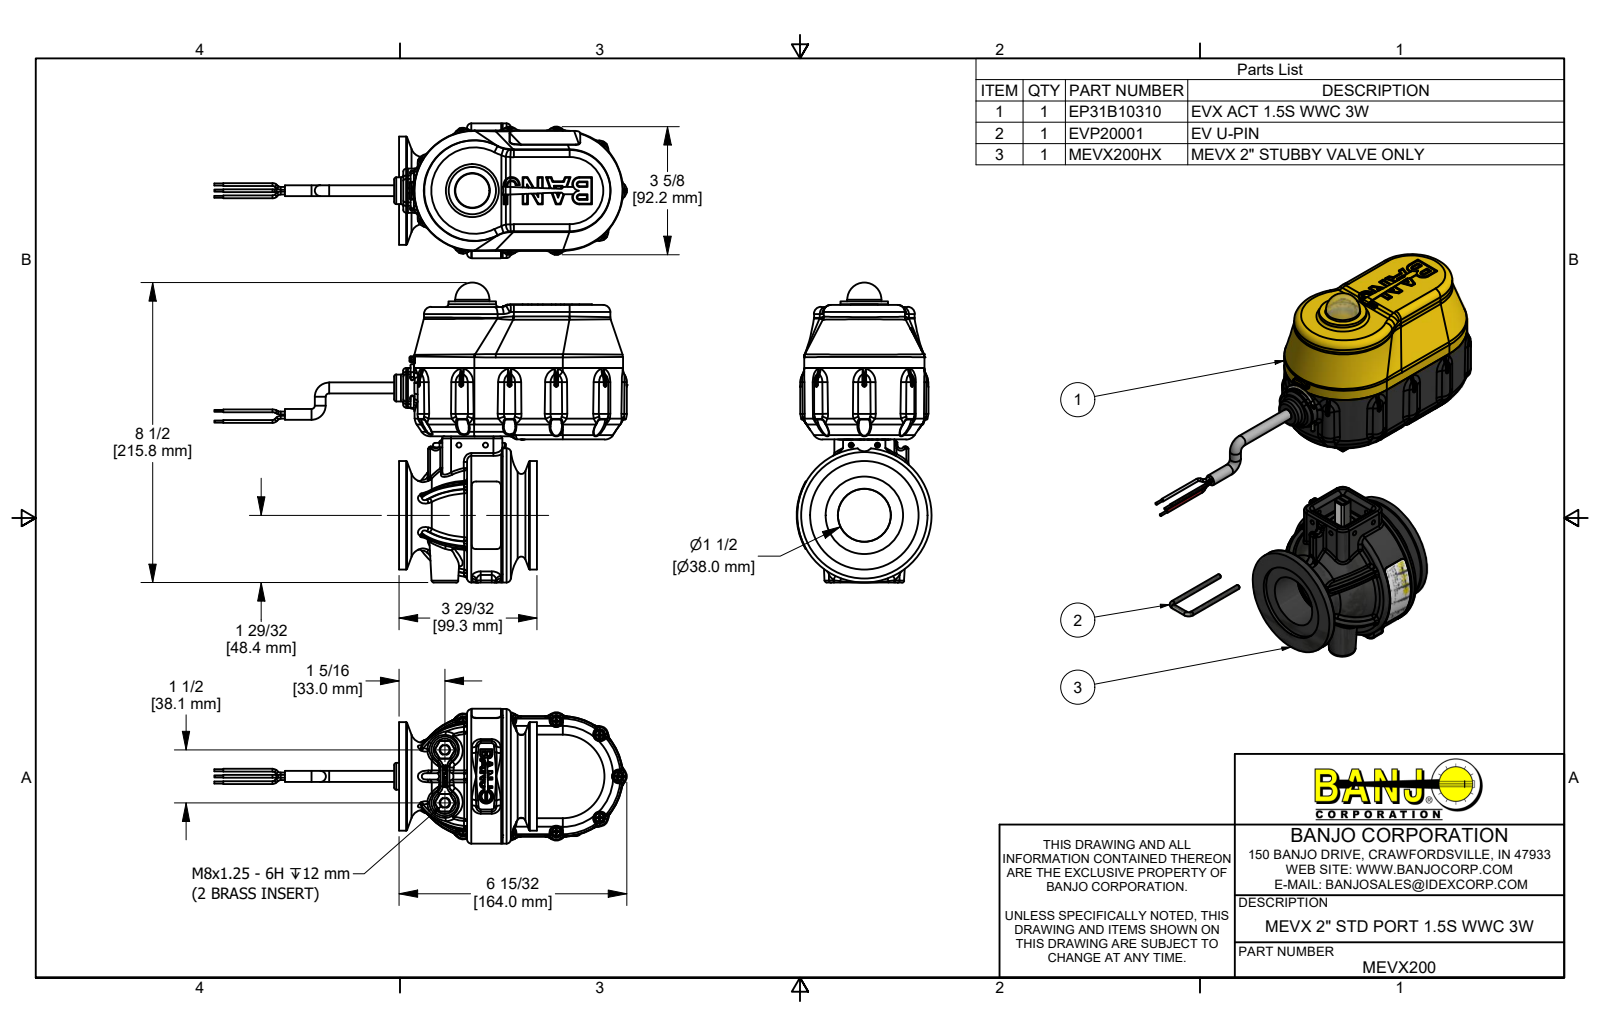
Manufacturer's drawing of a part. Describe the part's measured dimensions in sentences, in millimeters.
The part is named "MEVX200; EP31B10310; B61905PPHS; B632038PM (+8 more)". Its 3-D file was written by "Autodesk Inventor 2019 (AUTOMOTIVE_DESIGN)". It is 84 solids with 10997 faces: 3000 planar, 3122 cylindrical and 4875 other. Overall it measures 296.8 by 215.8 by 97.1 millimeters. Its volume is 839 800 cubic millimeters and its surface area 376 300 square millimeters. Round holes: 11 of diameter 2.4, 11 of diameter 3.8, 7 of diameter 2, 5 of diameter 3.4, 4 of diameter 2.7, 4 of diameter 3.2, 4 of diameter 3.5, 4 of diameter 3.8, 4 of diameter 3.8, 4 of diameter 4.3, 2 of diameter 2.7, 2 of diameter 3. Round bosses or shafts: 17 of diameter 6.4, 15 of diameter 2, 11 of diameter 3.6, 11 of diameter 2.7, 11 of diameter 2.2, 6 of diameter 1.5, 4 of diameter 6.9, 4 of diameter 5.6. Partial cylindrical surfaces (rounded edges, fillets, slot ends): 180 of radius 0.3, 145 of radius 1, 92 of radius 0.3, 71 of radius 0.5, 53 of radius 0.1, 43 of radius 1.5, 30 of radius 0.8, 28 of radius 2. The main face-to-face distances are 2.5, 65.2, 1.5, 5.4, 3.8, 48.2, 46.6, 42.8, 14.5, 16. The hole center spacings are 51.4, 32.6, 68.3, 69, 42.2, 45.1, 69.3, 96.2.
